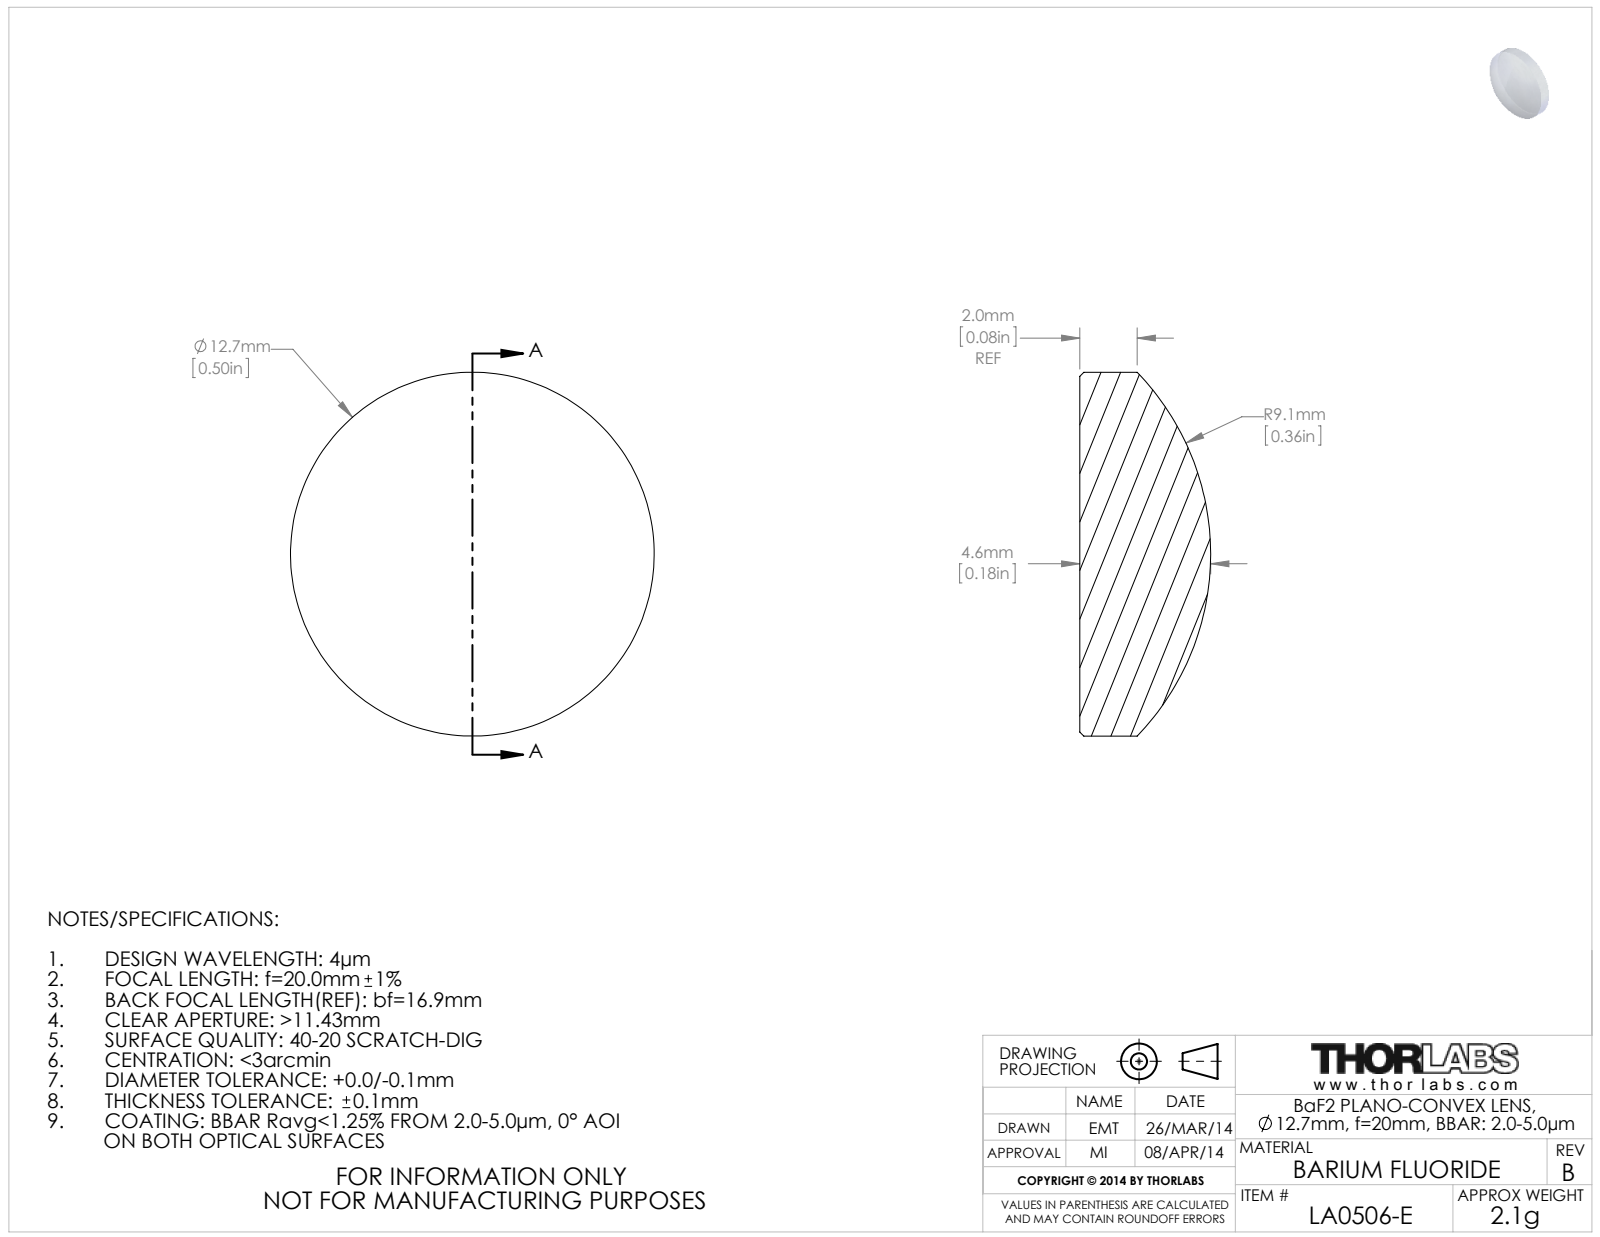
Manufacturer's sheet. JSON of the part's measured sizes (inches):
{"part_name": "20103-E0W", "step_written_by": "SolidWorks 2014 (CONFIG_CONTROL_DESIGN)", "units": "inches", "bodies": {"solids": 1, "faces": 7, "planar": 1, "cylindrical": 2, "other": 4}, "overall_size": [0.5, 0.5, 0.18], "volume_in3": 0.026, "surface_area_in2": 0.544, "round_bosses_or_shafts": [[0.5, 1]]}
